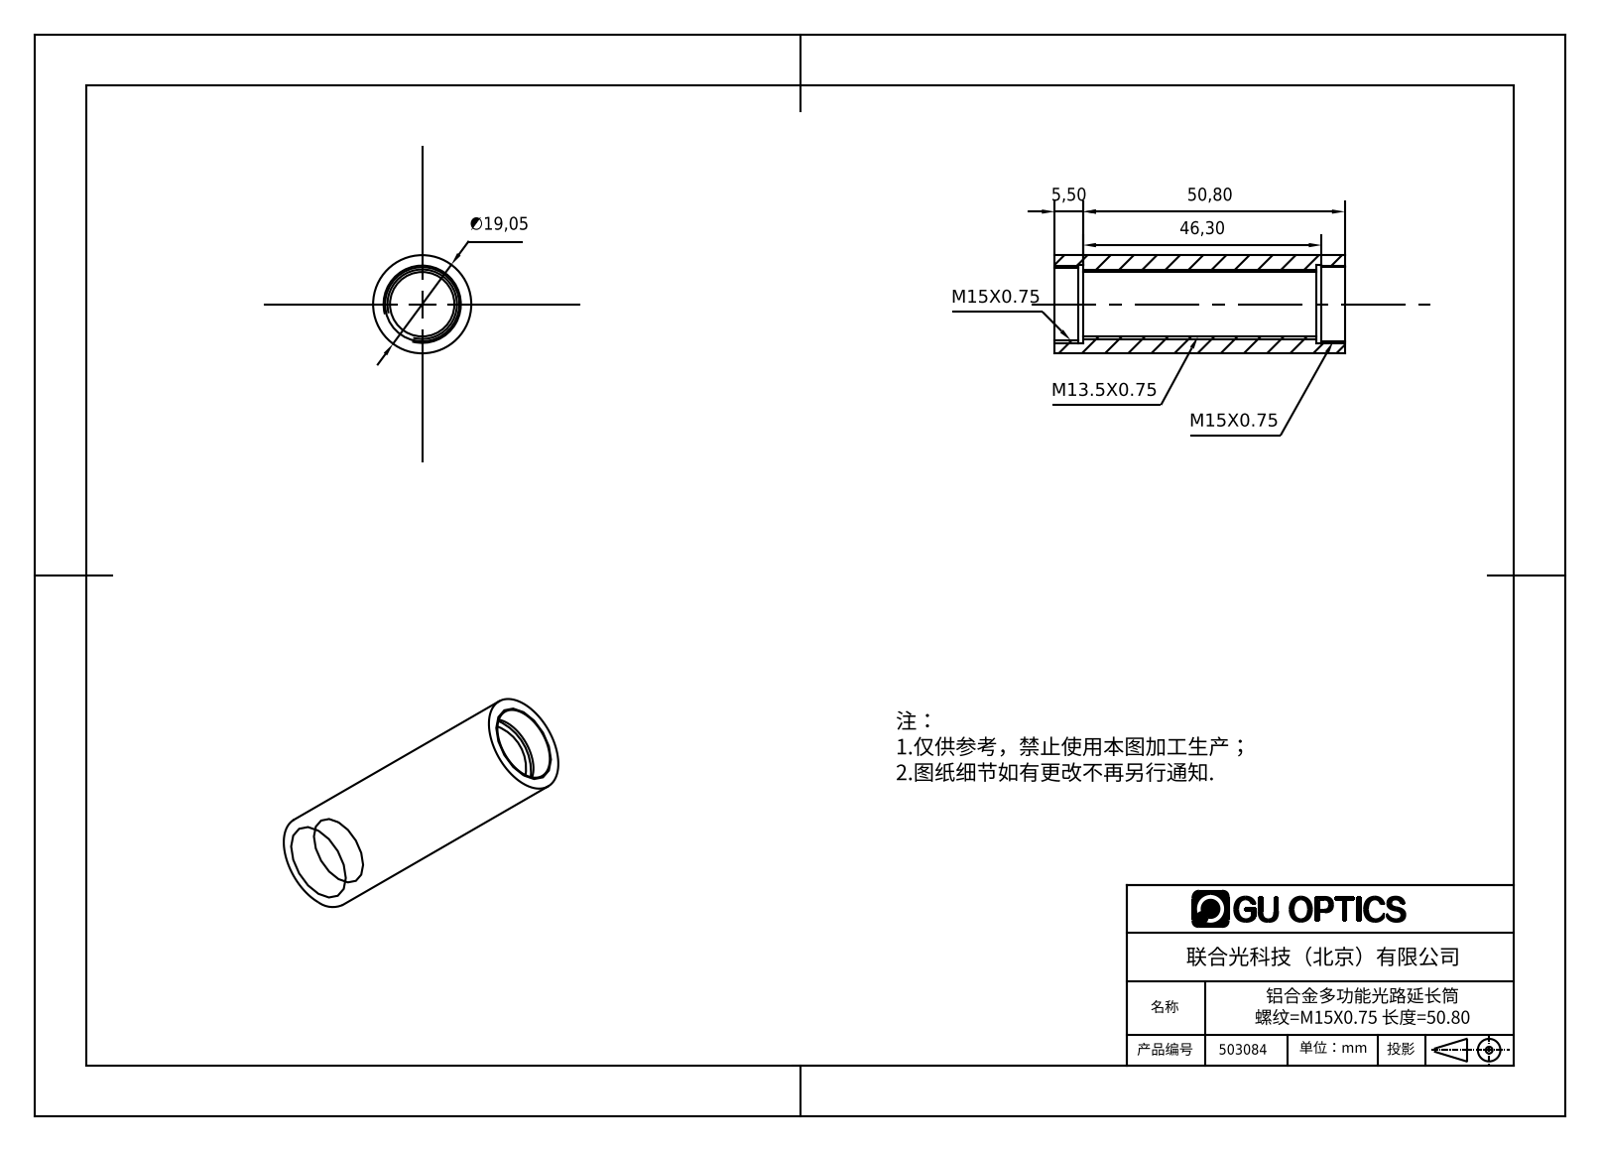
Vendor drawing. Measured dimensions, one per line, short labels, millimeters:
name: 503084
written by: SolidWorks 2016 (AUTOMOTIVE_DESIGN)
unit: mm
bodies: 1 solid, 18 faces (6 planar, 12 cylindrical, 0 other)
size: 56.3 × 19.05 × 19.05
volume: 8 699 mm³; area: 6 062 mm²
holes: 1× ⌀12.5, 1× ⌀14, 1× ⌀14.4, 1× ⌀15.2
bosses: 1× ⌀19.05
face distances: 56.3, 5.5, 50.8, 45.3, 4.5, 51.8, 1, 46.3, 47.3
